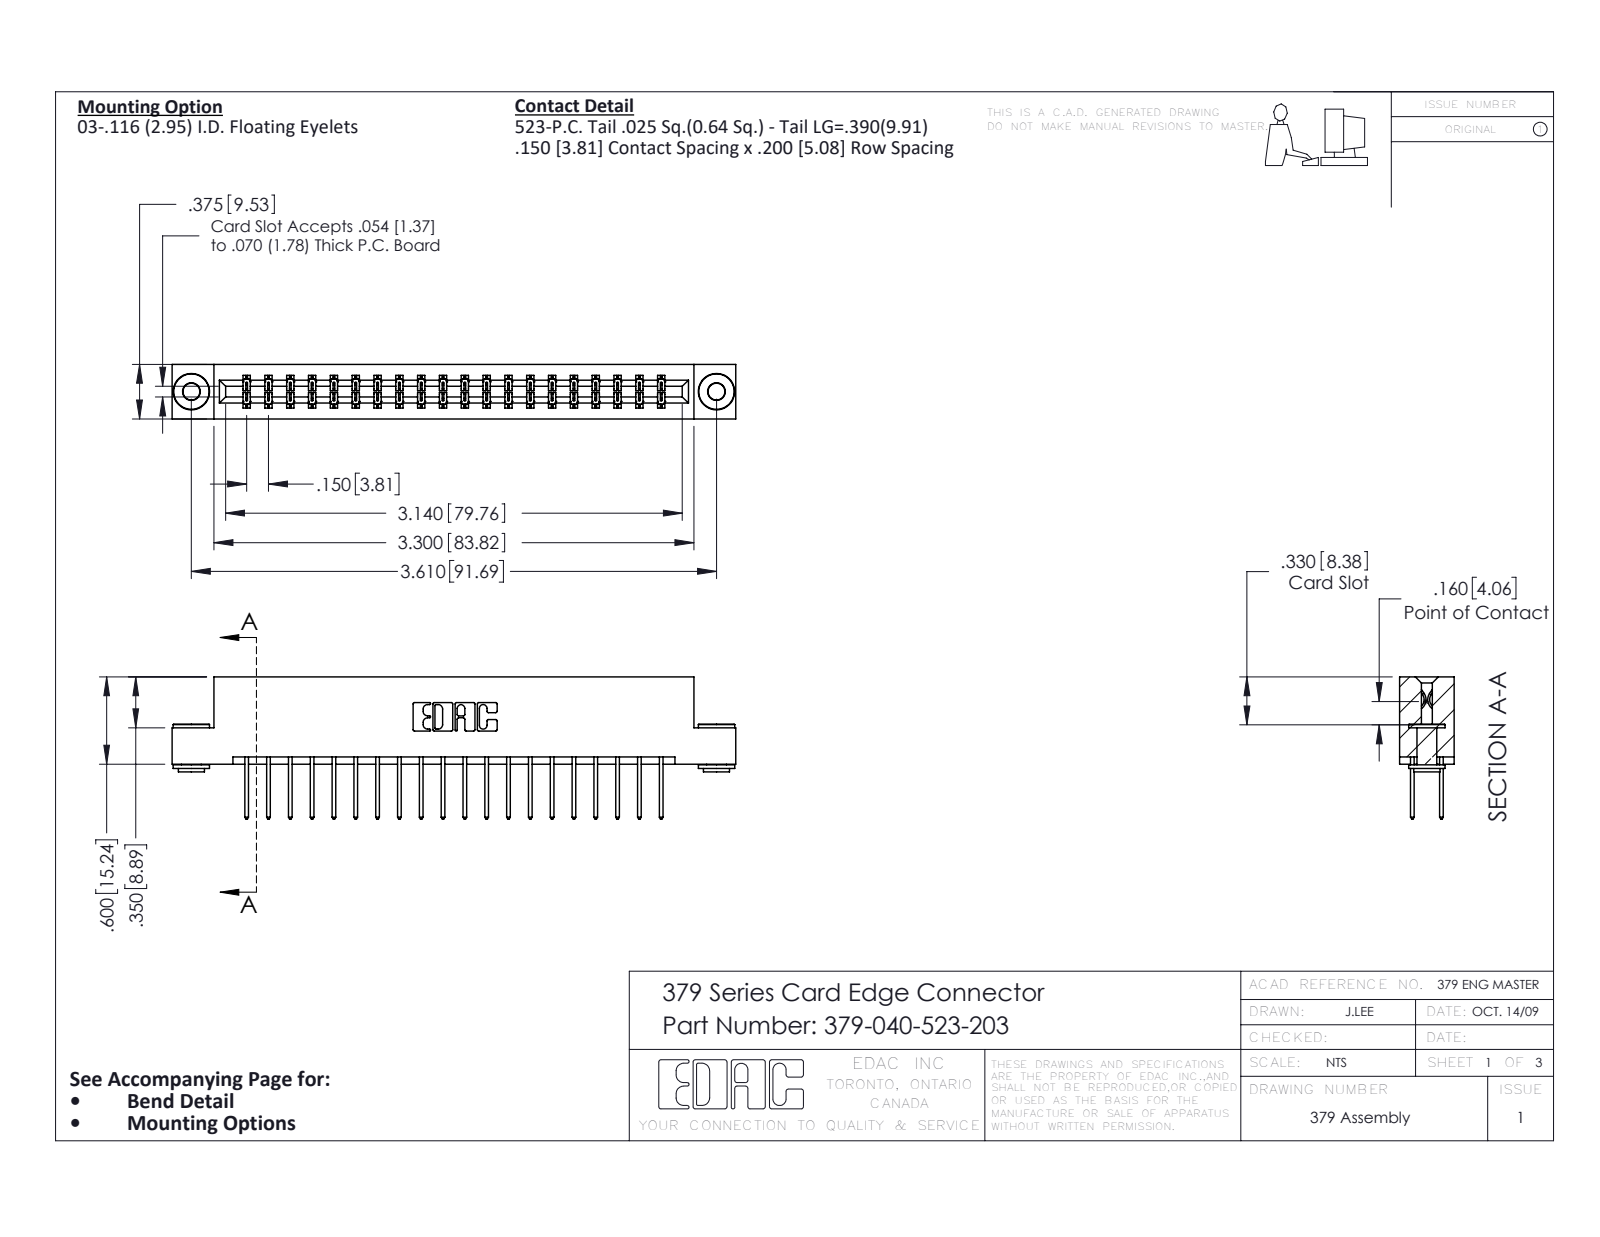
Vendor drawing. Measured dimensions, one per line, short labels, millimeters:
name: 379 Part_Flush - .156 Dia - TH; 379-040-523-203; 345-292-001_345-293-123; 345-250-002_345-250-002-102
written by: SolidWorks 2016 (CONFIG_CONTROL_DESIGN)
unit: mm
bodies: 43 solids, 2232 faces (1520 planar, 704 cylindrical, 8 other)
size: 98.4 × 24.8 × 9.5
volume: 10 300 mm³; area: 11 990 mm²
holes: 2× ⌀2.9, 2× ⌀4
bosses: 2× ⌀6.4, 2× ⌀4.6, 2× ⌀3.5
rounds: 60× R0.2, 40× R0.3, 22× R0.3, 6× R0.2, 6× R0.8, 3× R0.7, 2× R0.4, 2× R0.6
face distances: 7.6, 1.9, 5.1, 9.5, 2.5, 7, 0.6, 5.7, 1.9, 3.8
hole spacings: 91.7
